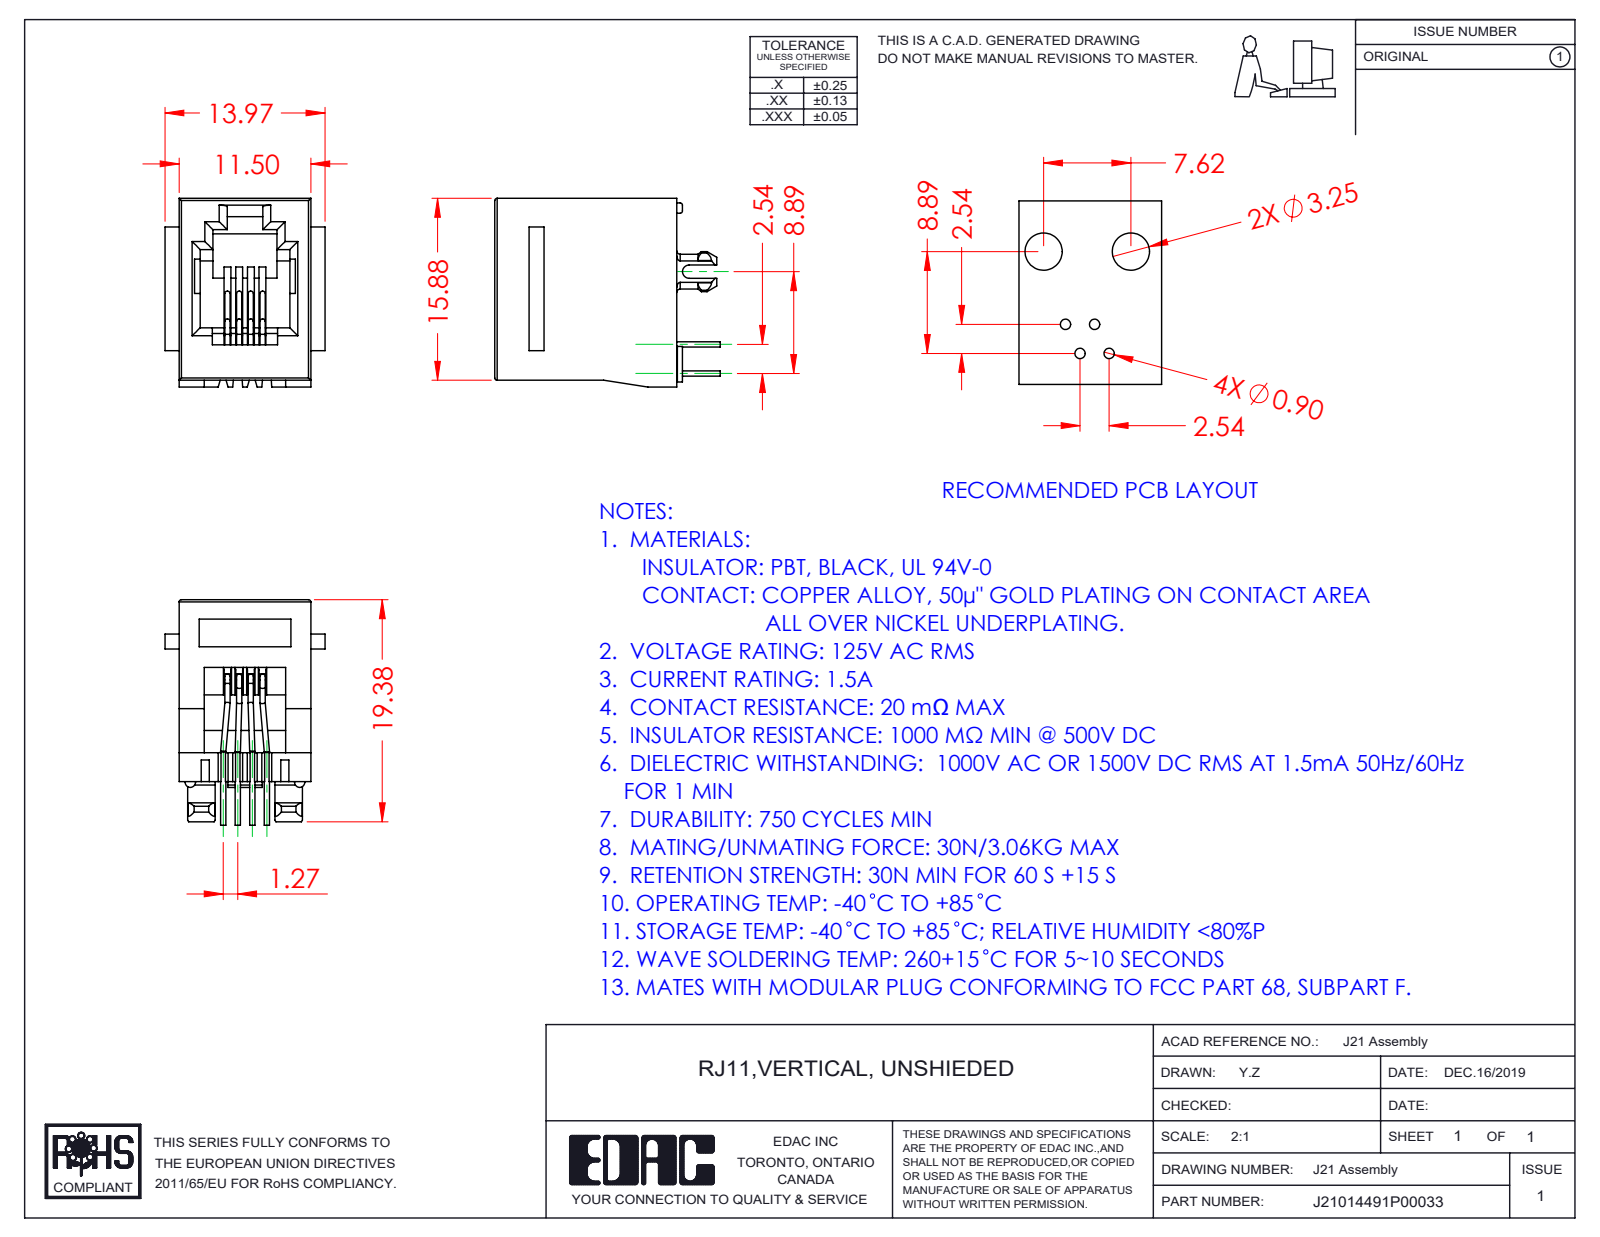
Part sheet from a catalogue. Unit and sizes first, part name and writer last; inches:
Units: inches
Overall size (bounding box): 0.775 × 0.649 × 0.55
Round holes (diameter × count): ⌀0.079 ×2
Round bosses / shafts (diameter × count): ⌀0.018 ×24
Partial cylindrical surfaces — rounded edges, fillets, slot ends (radius × count): R0.02 ×9, R0.028 ×9, R0.008 ×7, R0.009 ×4, R0.018 ×2, R0.06 ×2, R0.069 ×2, R0.022 ×1
Main face-to-face distances: 0.453, 0.063, 0.625, 0.04, 0.283, 0.024, 0.116, 0.337, 0.08, 0.053
Hole centre spacings: 0.331
Volume: 0.099 in³ · Surface area: 3.974 in²
Bodies: 5 solids, 369 faces (230 planar, 111 cylindrical, 28 other)
Part name (STEP PRODUCT): 21 Insulator; 21 Contacts; RJ21014491P00033
STEP written by: SolidWorks 2016 (CONFIG_CONTROL_DESIGN)
